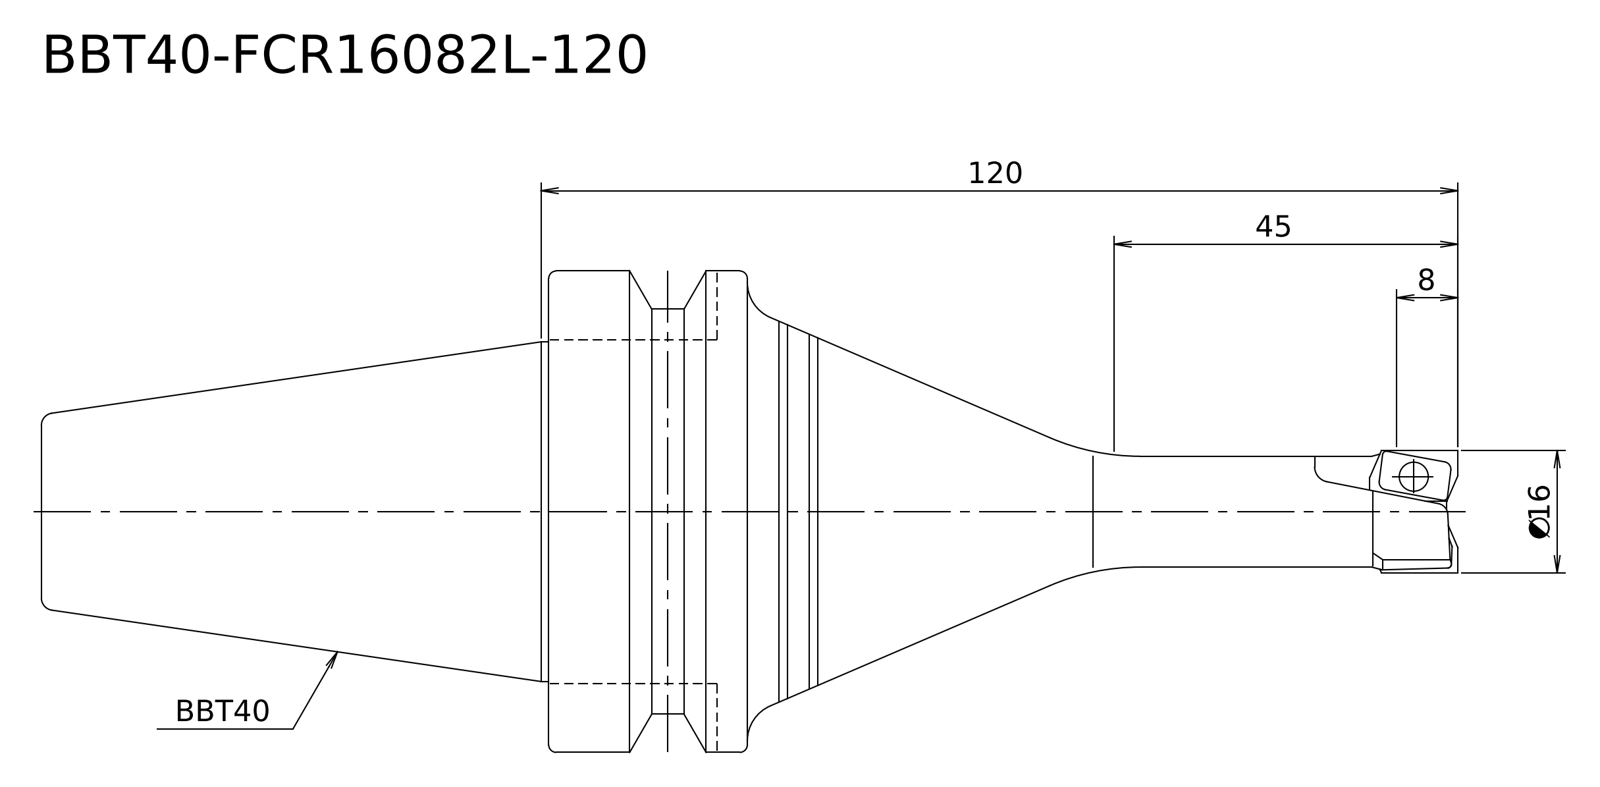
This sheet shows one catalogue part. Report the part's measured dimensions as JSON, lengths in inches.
{"step_written_by": "Kubotek KeyCreator V8.5.1 (14335) (CONFIG_CONTROL_DESIGN)", "units": "inches", "bodies": {"solids": 1, "faces": 17, "planar": 4, "cylindrical": 6, "other": 7}, "overall_size": [7.299, 2.48, 2.48], "volume_in3": 11.91, "surface_area_in2": 36.98, "round_bosses_or_shafts": [[2.48, 1], [2.087, 1], [1.75, 1], [0.63, 1], [0.571, 1]], "face_to_face_distances": [2.614, 1.024, 3.638, 3.661, 4.685, 7.299]}
